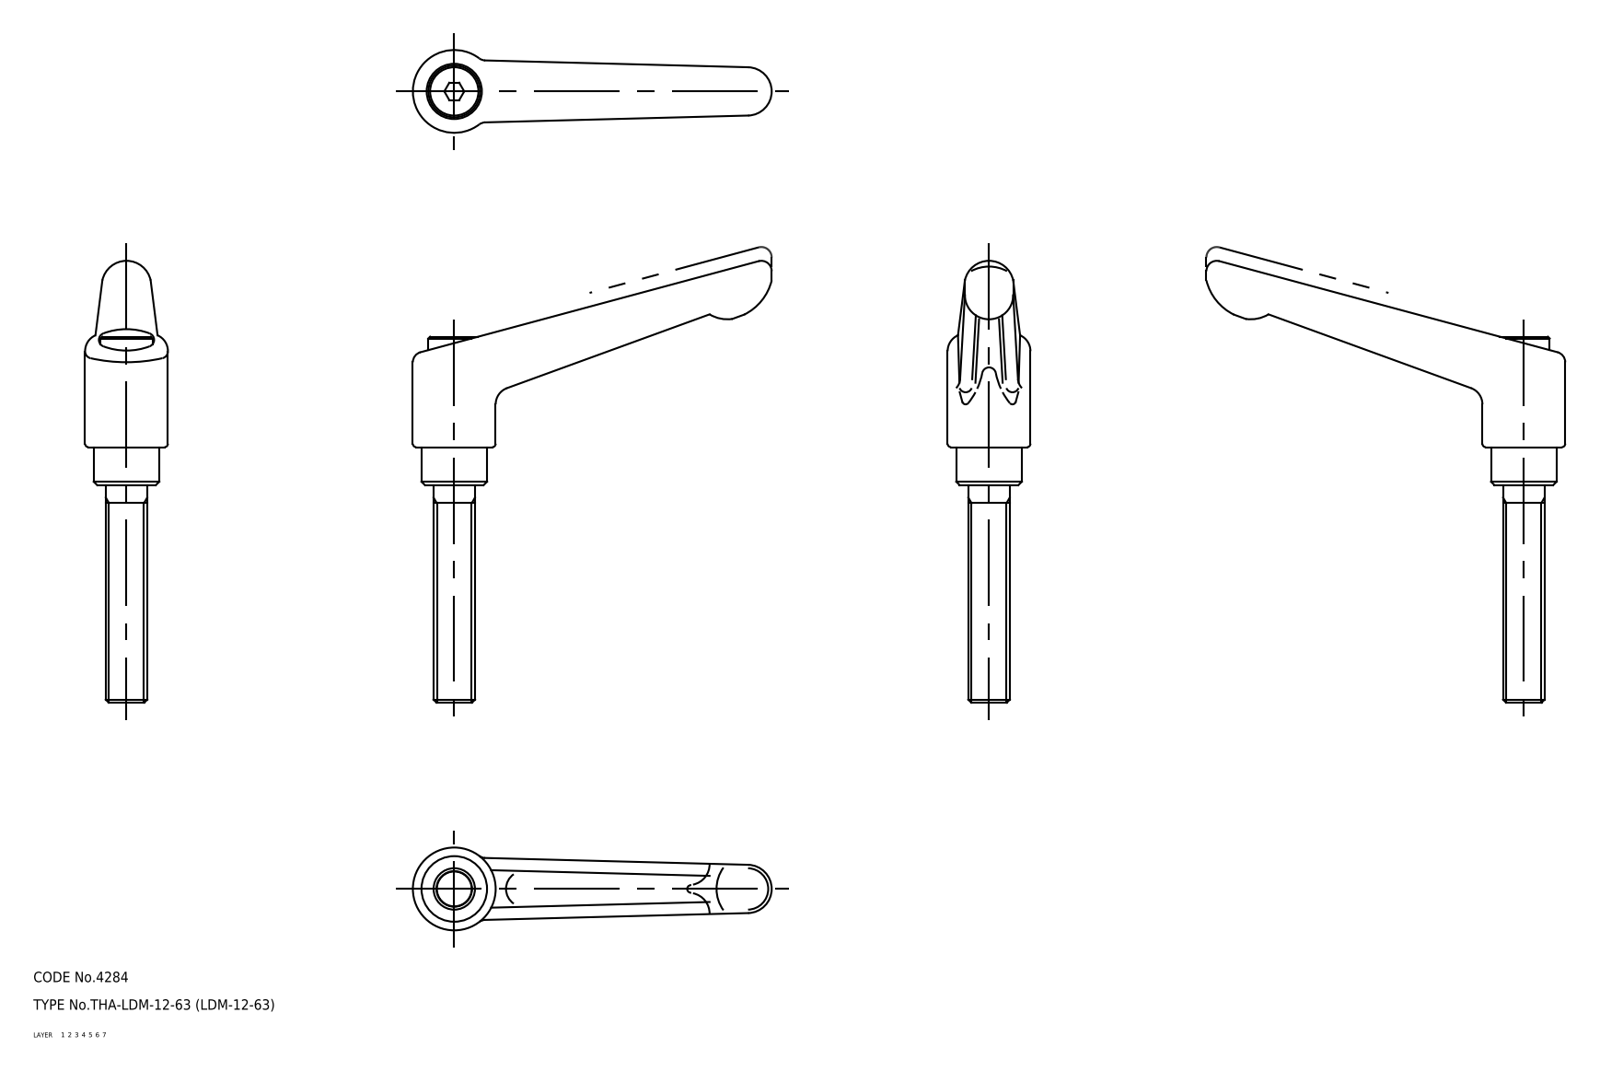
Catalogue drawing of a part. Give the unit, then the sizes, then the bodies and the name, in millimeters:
Units: millimetres
Overall size (bounding box): 128 × 104 × 24
Volume: 35 164 mm³ · Surface area: 14 598 mm²
Bodies: 3 solids, 96 faces (0 planar, 0 cylindrical, 96 other)
Part name (STEP PRODUCT): sleeve; screw; handle; LDM_12_63_12081_36
STEP written by: CADfix (AUTOMOTIVE_DESIGN)
